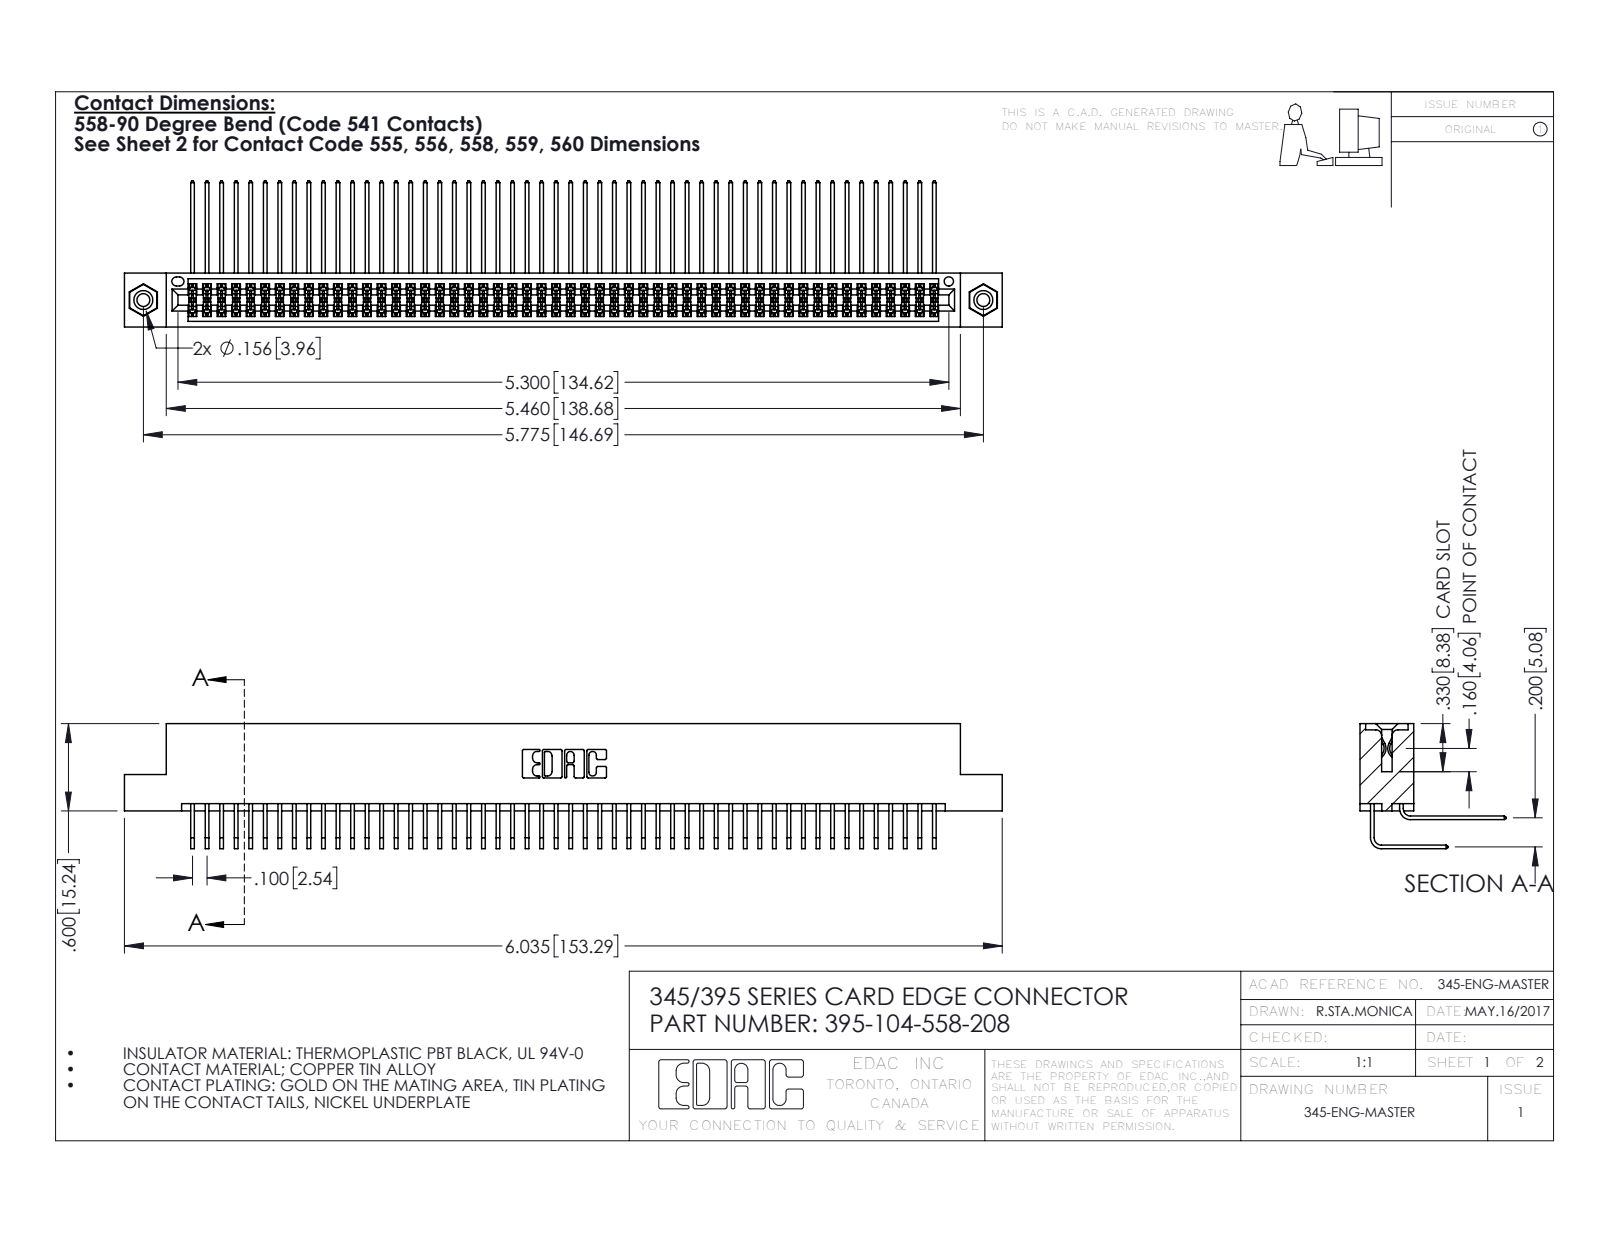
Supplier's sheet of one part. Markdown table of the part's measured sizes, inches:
| quantity | value |
| --- | --- |
| part name | 345-250-001_345-250-003-102; 345-292-001_558 559 Tail - 1; 395-104-558-208; 345-292-001_558 Tail - 2 (+1 more) |
| STEP written by | SolidWorks 2016 (CONFIG_CONTROL_DESIGN) |
| units | inches |
| bodies | 107 solids, 5594 faces (3752 planar, 1826 cylindrical, 16 other) |
| overall size | 6.035 × 1.005 × 0.859 |
| volume | 0.951 in³ |
| surface area | 40.38 in² |
| round holes (diameter × count) | 0.089 × 2, 0.125 × 2, 0.156 × 2, 0.064 × 1 |
| round bosses / shafts (diameter × count) | 0.155 × 2 |
| partial cylindrical surfaces (radius × count) | 0.006 × 157, 0.01 × 22, 0.007 × 6, 0.031 × 6, 0.026 × 3, 0.014 × 2, 0.019 × 2, 0.022 × 2 |
| main face-to-face distances | 0.072, 0.298, 0.2, 0.37, 0.098, 0.272, 0.025, 0.225, 0.025, 0.175 |
| hole center spacings | 0.27, 5.539, 5.775 |
